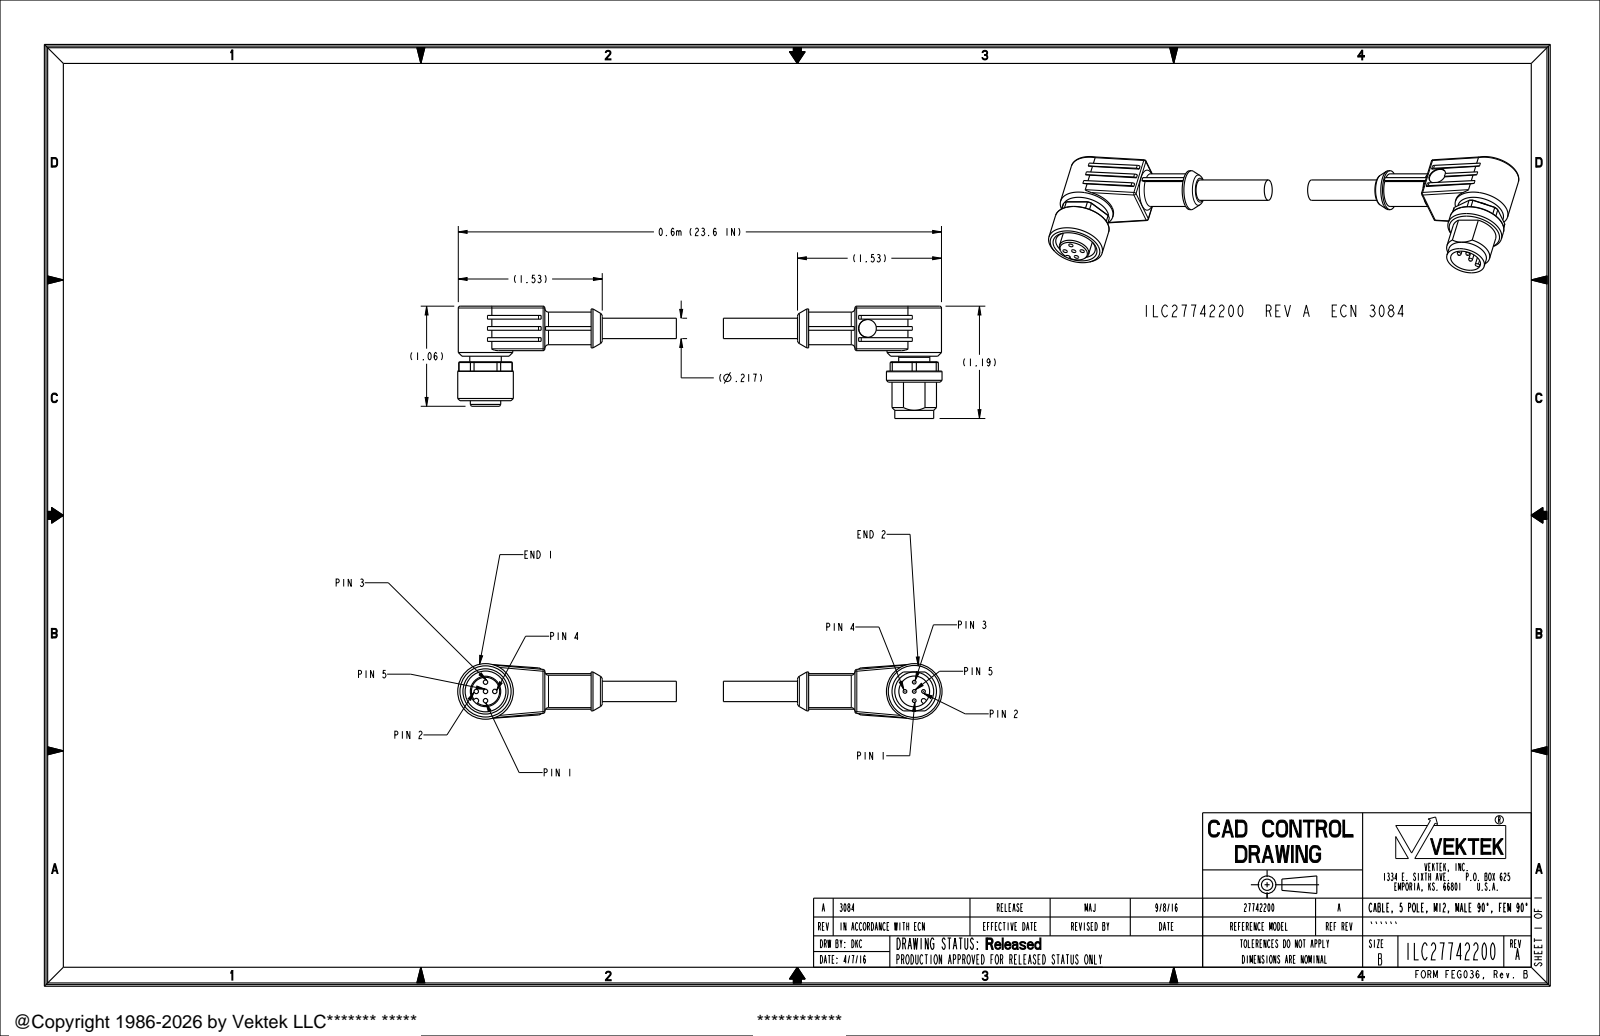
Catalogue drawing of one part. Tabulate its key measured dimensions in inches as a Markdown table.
| quantity | value |
| --- | --- |
| part name | 27742200_1; 27742200_2; ILC27742200 |
| STEP written by | PRO/ENGINEER BY PARAMETRIC TECHNOLOGY CORPORATION, 2013320 (AUTOMOTIVE_DESIGN) |
| units | inches |
| bodies | 2 solids, 306 faces (125 planar, 104 cylindrical, 77 other) |
| overall size | 5.146 × 1.193 × 0.591 |
| volume | 0.828 in³ |
| surface area | 10.95 in² |
| round holes (diameter × count) | 0.047 × 5, 0.189 × 2, 0.327 × 1, 0.433 × 1 |
| round bosses / shafts (diameter × count) | 0.039 × 5, 0.591 × 2, 0.579 × 2, 0.413 × 2, 0.346 × 1, 0.335 × 1, 0.333 × 1, 0.331 × 1 |
| partial cylindrical surfaces (radius × count) | 0.02 × 16, 0.039 × 4, 0.283 × 2, 0.024 × 1, 0.026 × 1, 0.236 × 1 |
| main face-to-face distances | 0.472, 0.059, 0.118, 0.591, 0.531, 0.176, 0.217, 0.098, 0.374, 0.256 |
| hole center spacings | 0.098, 0.139, 0.197, 4.556, 3.591, 4.457, 4.555, 4.654 |
